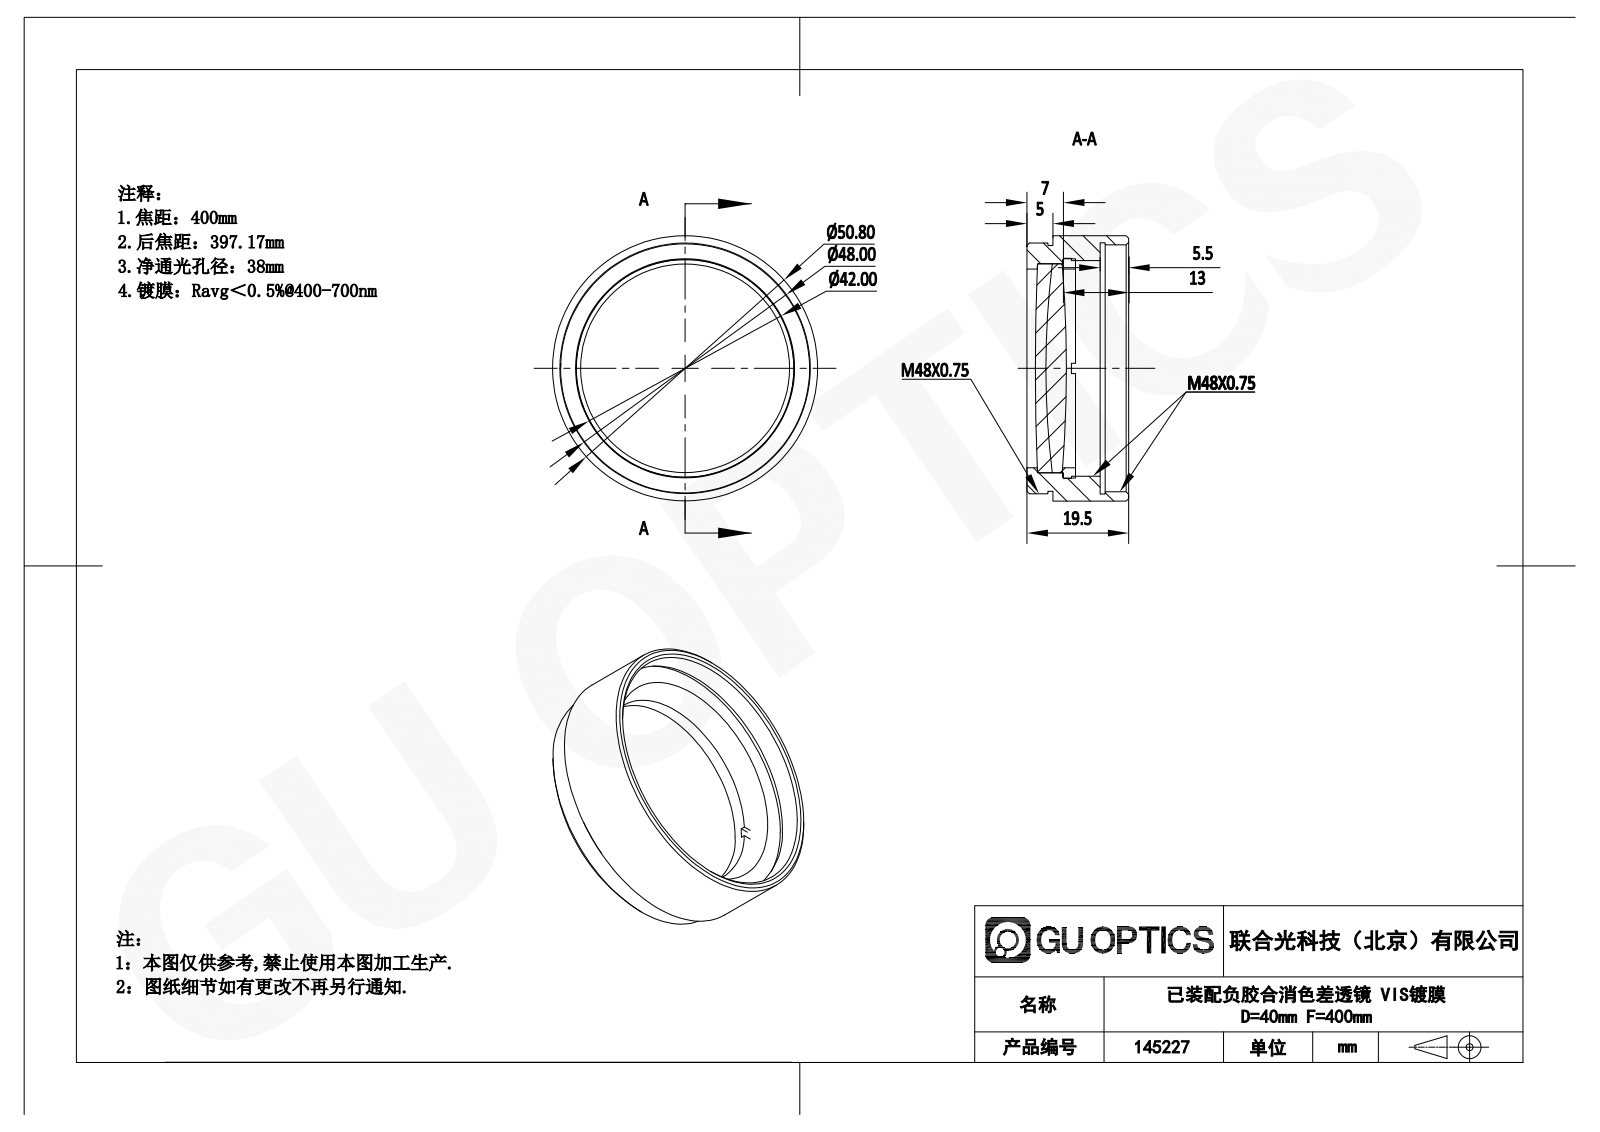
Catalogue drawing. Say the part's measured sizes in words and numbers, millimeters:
The part is named "GL31-040-400-VIS_Solidworks; APD-ML40-400-VIS-A; M42x0.75ѹȦ". Its 3-D file was written by "SolidWorks 2022 (AUTOMOTIVE_DESIGN)". It is 4 solids with 64 faces: 18 planar, 26 cylindrical and 20 other. Overall it measures 50.8 by 50.8 by 19.5 millimeters. Its volume is 17 914 cubic millimeters and its surface area 14 423 square millimeters. Round holes: 1 of diameter 38, 1 of diameter 41.25, 1 of diameter 42.1, 1 of diameter 47.25, 1 of diameter 48.1. Round bosses or shafts: 1 of diameter 50.8, 1 of diameter 48, 1 of diameter 47, 1 of diameter 42, 1 of diameter 40. The main face-to-face distances are 14, 5, 2, 9, 7, 9.32, 4.32, 4.68, 6.82, 1.82.
